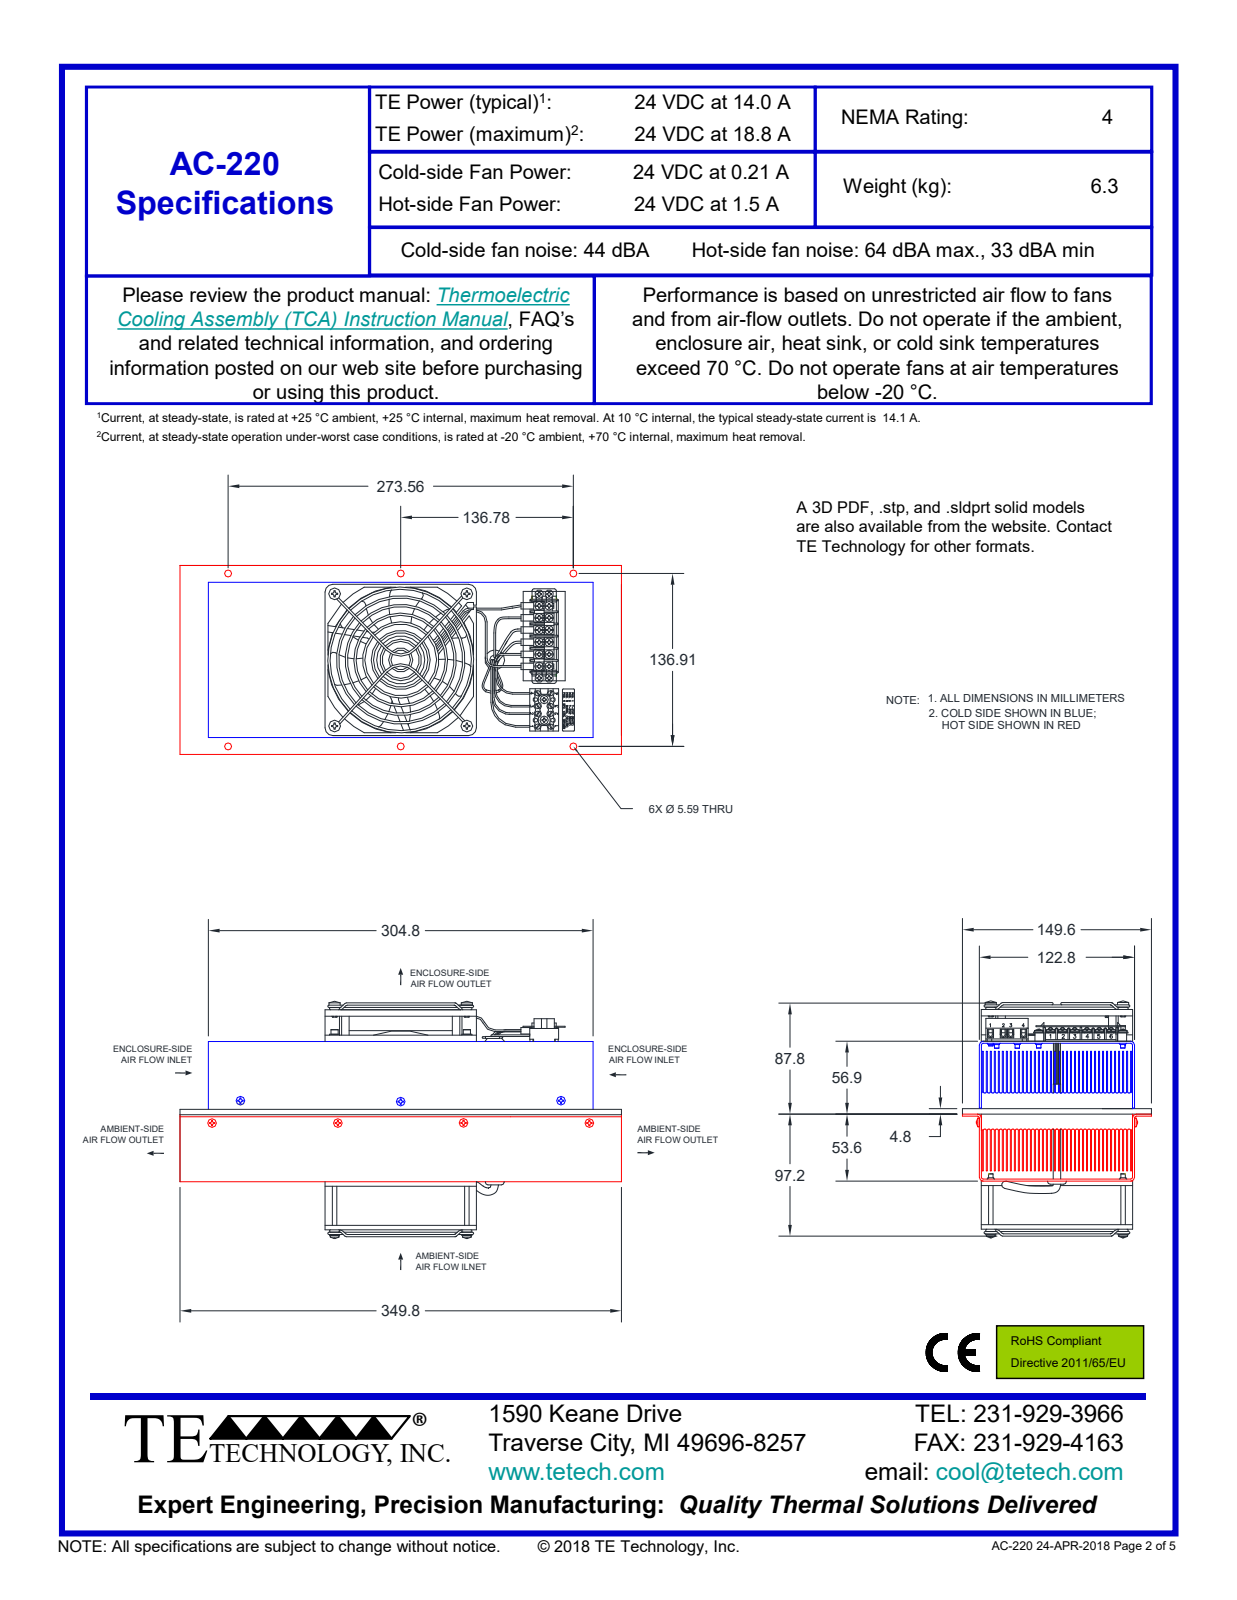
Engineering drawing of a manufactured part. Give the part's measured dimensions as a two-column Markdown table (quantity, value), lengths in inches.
| quantity | value |
| --- | --- |
| part name | heat sink AC-220; thermal pad AC-220; dummy module 39 tall no wires; thermostat TO220 style (+8 more) |
| STEP written by | Alibre (AUTOMOTIVE_DESIGN) |
| units | inches |
| bodies | 220 solids, 4091 faces (2482 planar, 582 cylindrical, 1027 other) |
| overall size | 13.77 × 7.282 × 5.89 |
| volume | 138.9 in³ |
| surface area | 3 617 in² |
| round holes (diameter × count) | 0.104 × 45, 0.22 × 23, 0.164 × 12, 0.166 × 12, 0.168 × 12, 0.438 × 12, 0.17 × 8, 0.18 × 8, 0.185 × 4, 0.32 × 4, 0.38 × 3, 0.085 × 2 |
| round bosses / shafts (diameter × count) | 0.138 × 49, 0.27 × 31, 0.071 × 18, 0.375 × 14, 0.406 × 12, 0.248 × 12, 0.226 × 12, 0.06 × 8 |
| partial cylindrical surfaces (radius × count) | 0.038 × 21, 0.05 × 18, 0.01 × 16, 0.015 × 8, 0.03 × 8, 0.078 × 8, 0.275 × 8, 0.063 × 6 |
| main face-to-face distances | 0.154, 0.063, 0.246, 0.123, 4.773, 0.031, 0.369, 0.159, 0.215, 0.123 |
| hole center spacings | 2.25, 2.316, 6.733, 7.099, 2.316, 3.924, 7.846, 2.25 |
